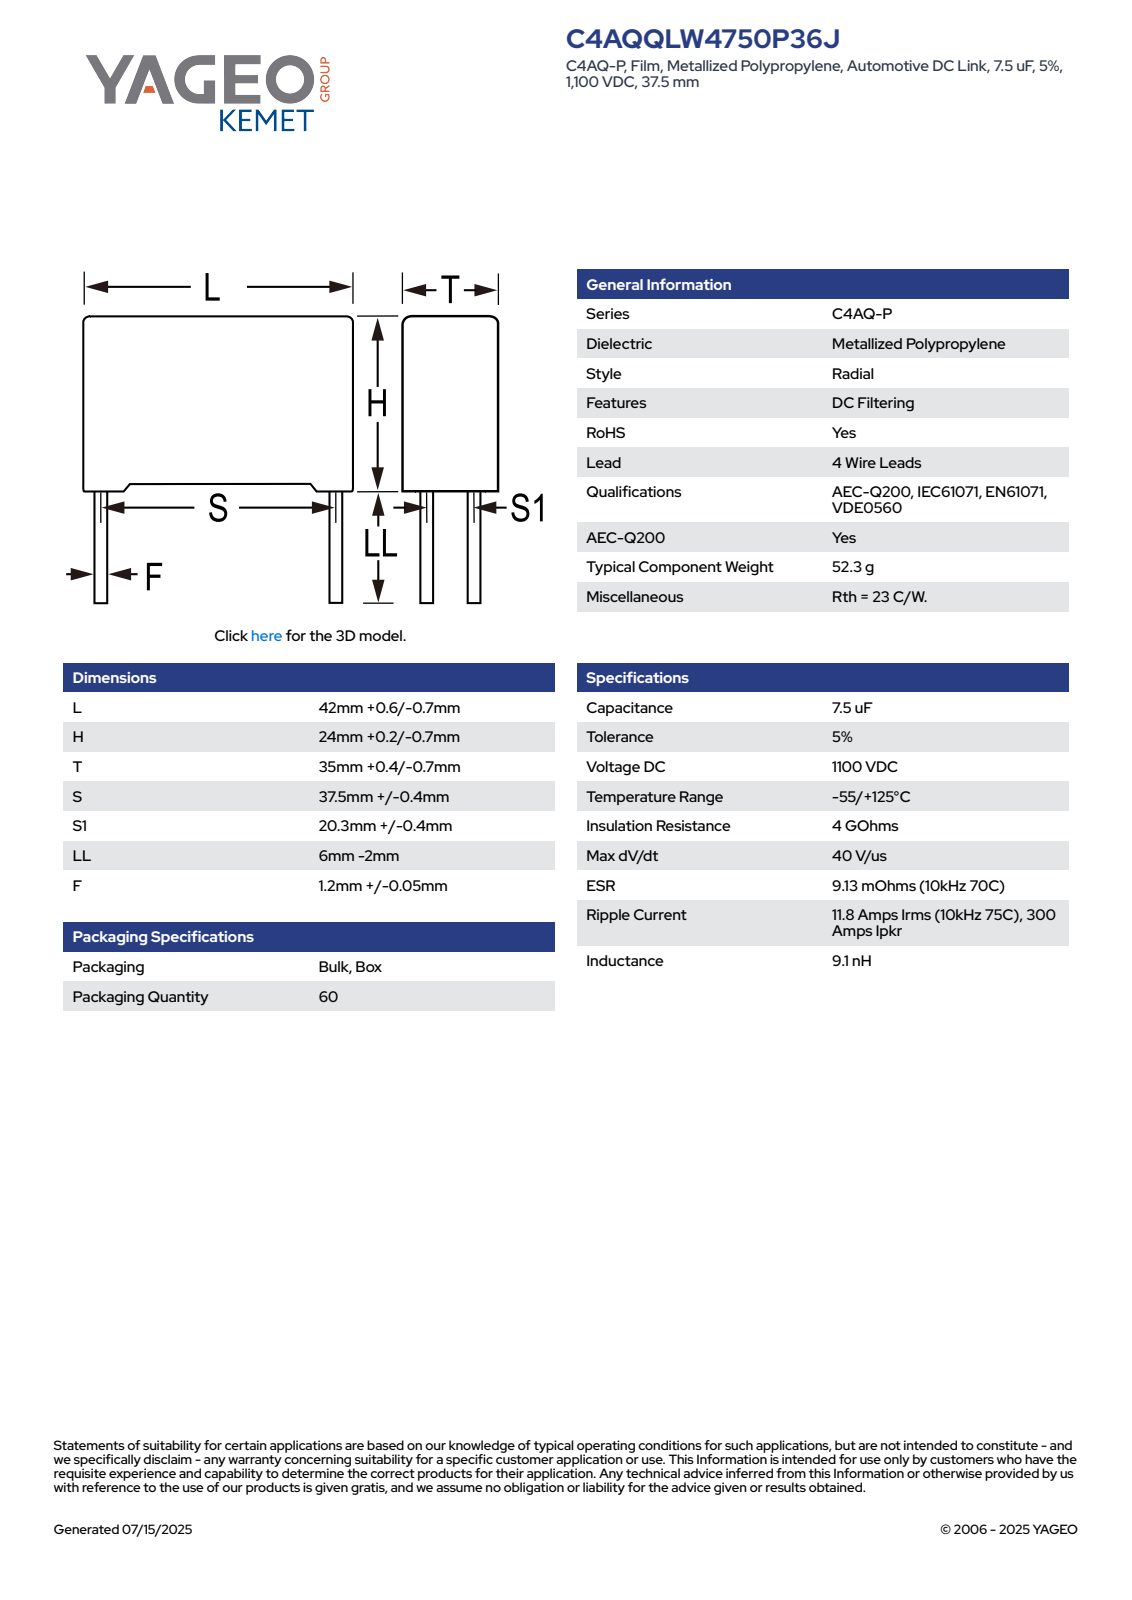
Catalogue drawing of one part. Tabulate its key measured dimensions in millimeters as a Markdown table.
| quantity | value |
| --- | --- |
| part name | CFP_RB4_42X24X35_L42.6H24.2T35.4S37.5S120.3LL4F1.25 |
| STEP written by | SolidWorks 2014 (AUTOMOTIVE_DESIGN) |
| units | millimeters |
| bodies | 4 solids, 91 faces (83 planar, 8 cylindrical, 0 other) |
| overall size | 42.6 × 35.41 × 28.2 |
| volume | 35 587 mm³ |
| surface area | 6 998 mm² |
| round bosses / shafts (diameter × count) | 1.25 × 4 |
| main face-to-face distances | 23.49, 35.4, 42.6, 0.71, 24.2, 35.41, 2.18, 40.42, 38.24, 33.22 |
